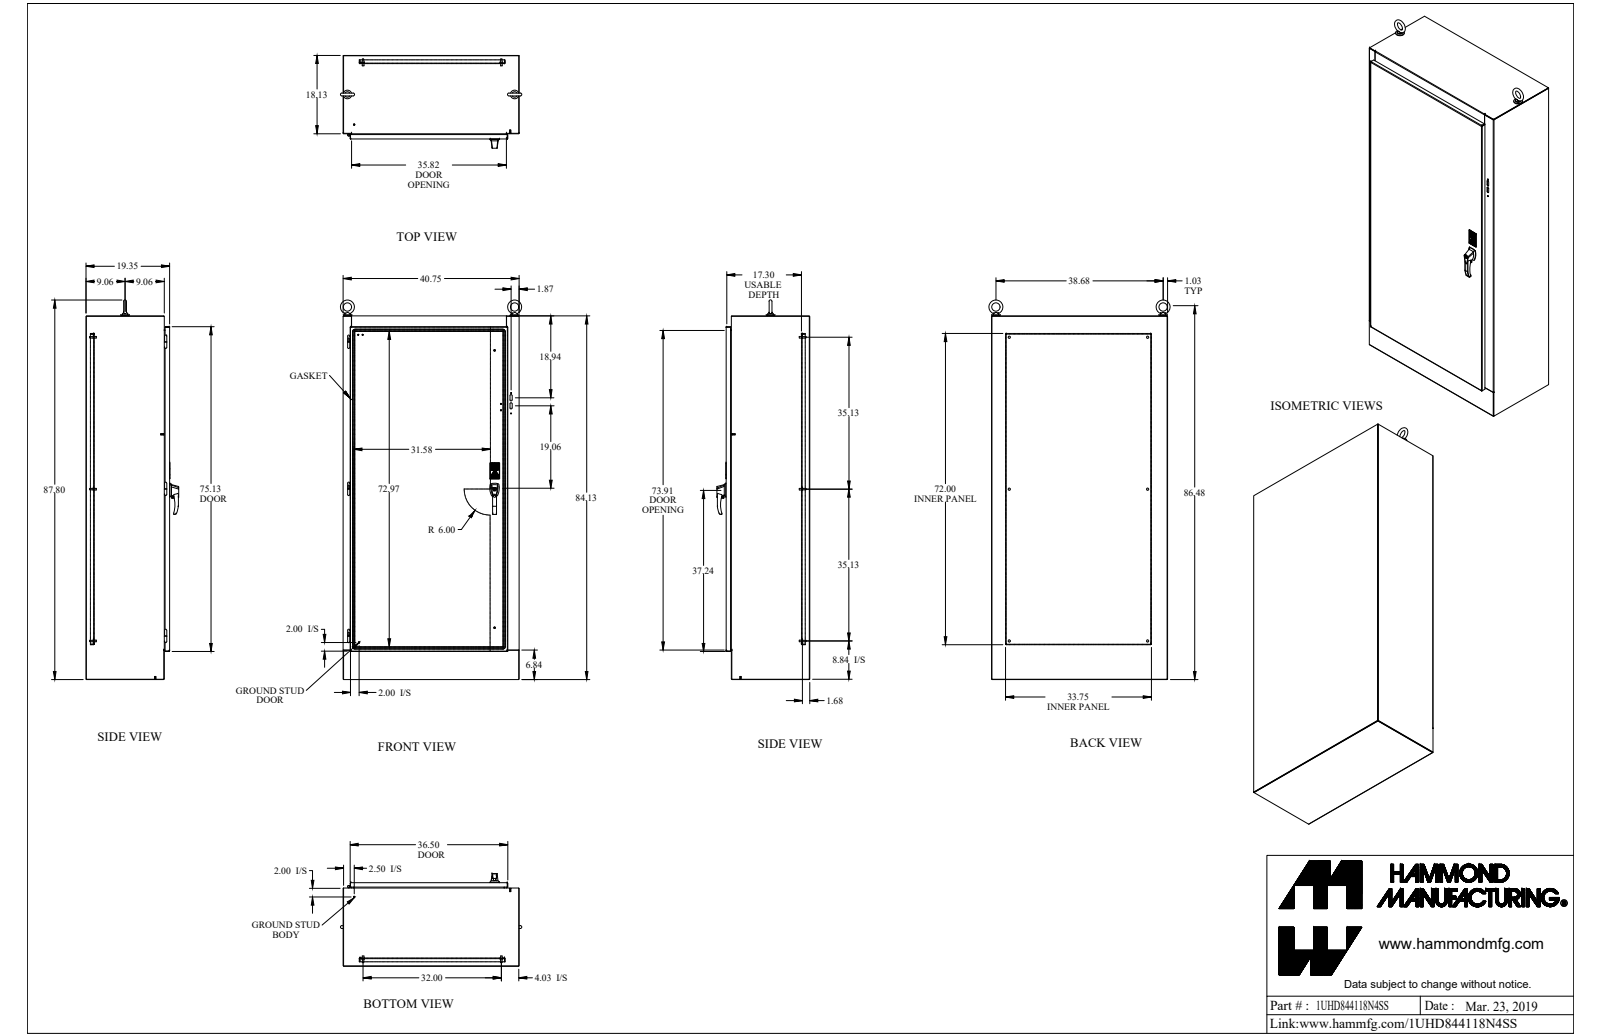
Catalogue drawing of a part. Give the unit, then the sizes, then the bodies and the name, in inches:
Units: inches
Overall size (bounding box): 87.799 × 41.932 × 21.464
Round holes (diameter × count): ⌀0.35 ×7, ⌀0.196 ×6, ⌀0.307 ×6, ⌀0.563 ×6, ⌀0.25 ×5, ⌀0.156 ×4, ⌀0.281 ×4, ⌀0.445 ×4, ⌀0.313 ×3, ⌀0.167 ×2, ⌀0.189 ×2, ⌀0.255 ×2
Round bosses / shafts (diameter × count): ⌀0.25 ×11, ⌀1 ×8, ⌀0.375 ×7, ⌀0.65 ×6, ⌀0.332 ×6, ⌀0.19 ×4, ⌀0.625 ×3, ⌀0.5 ×3
Partial cylindrical surfaces — rounded edges, fillets, slot ends (radius × count): R0.125 ×27, R0.048 ×24, R0.143 ×24, R0.5 ×23, R0.06 ×19, R0.25 ×19, R0.017 ×16, R0.032 ×12
Main face-to-face distances: 0.095, 19.254, 40.655, 19.159, 19.349, 0.125, 1.907, 1.812, 17.348, 17.443
Hole centre spacings: 32, 7.433, 7.467, 7.5, 12.875, 14.9, 21.601, 30.461
Volume: 1 624 in³ · Surface area: 32 370 in²
Bodies: 112 solids, 2003 faces (1132 planar, 535 cylindrical, 336 other)
Part name (STEP PRODUCT): 1UHD844118N4SS
STEP written by: SolidWorks 2018 (AUTOMOTIVE_DESIGN)
